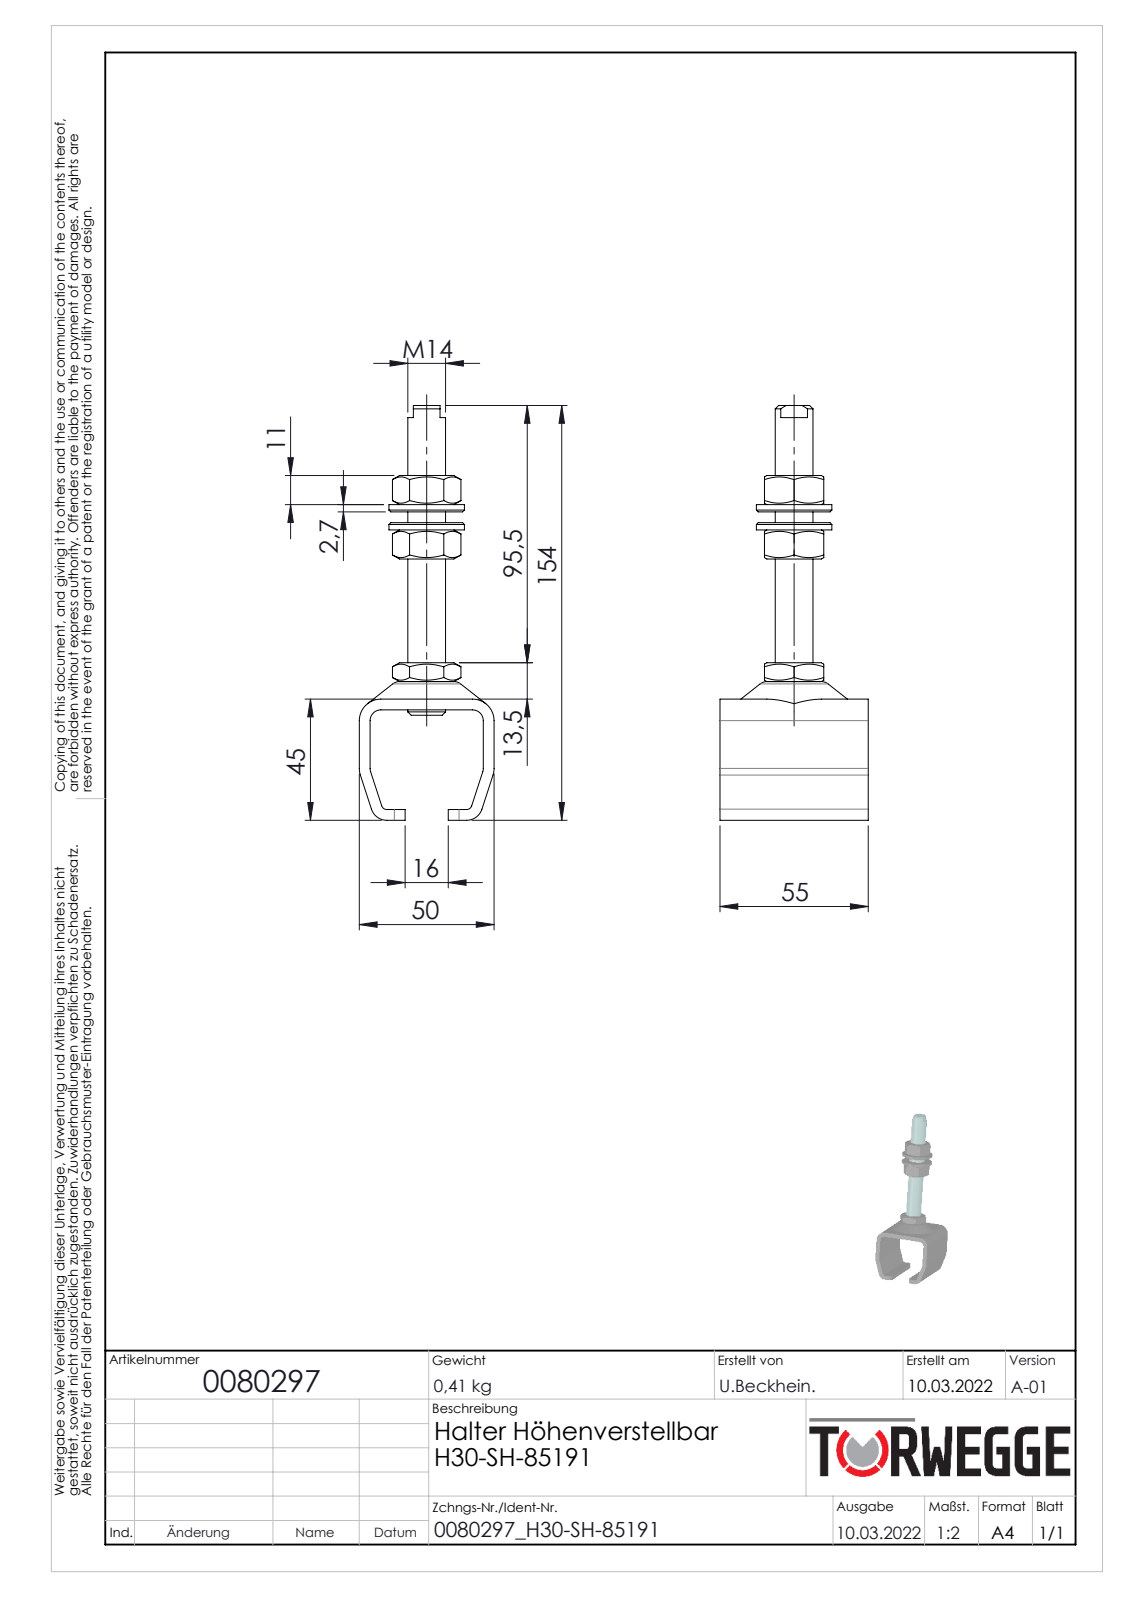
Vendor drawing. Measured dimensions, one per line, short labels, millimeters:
name: 0080297
written by: SolidWorks 2020 (AUTOMOTIVE_DESIGN)
unit: mm
bodies: 8 solids, 157 faces (70 planar, 34 cylindrical, 53 other)
size: 154 × 55 × 50
volume: 61 312 mm³; area: 31 053 mm²
holes: 1× ⌀11.83, 1× ⌀15
bosses: 1× ⌀28, 1× ⌀14
rounds: 8× R4, 4× R8, 2× R2, 2× R6
face distances: 4, 46, 41, 22, 50, 42, 69.5, 110.5, 2.7, 6.7
